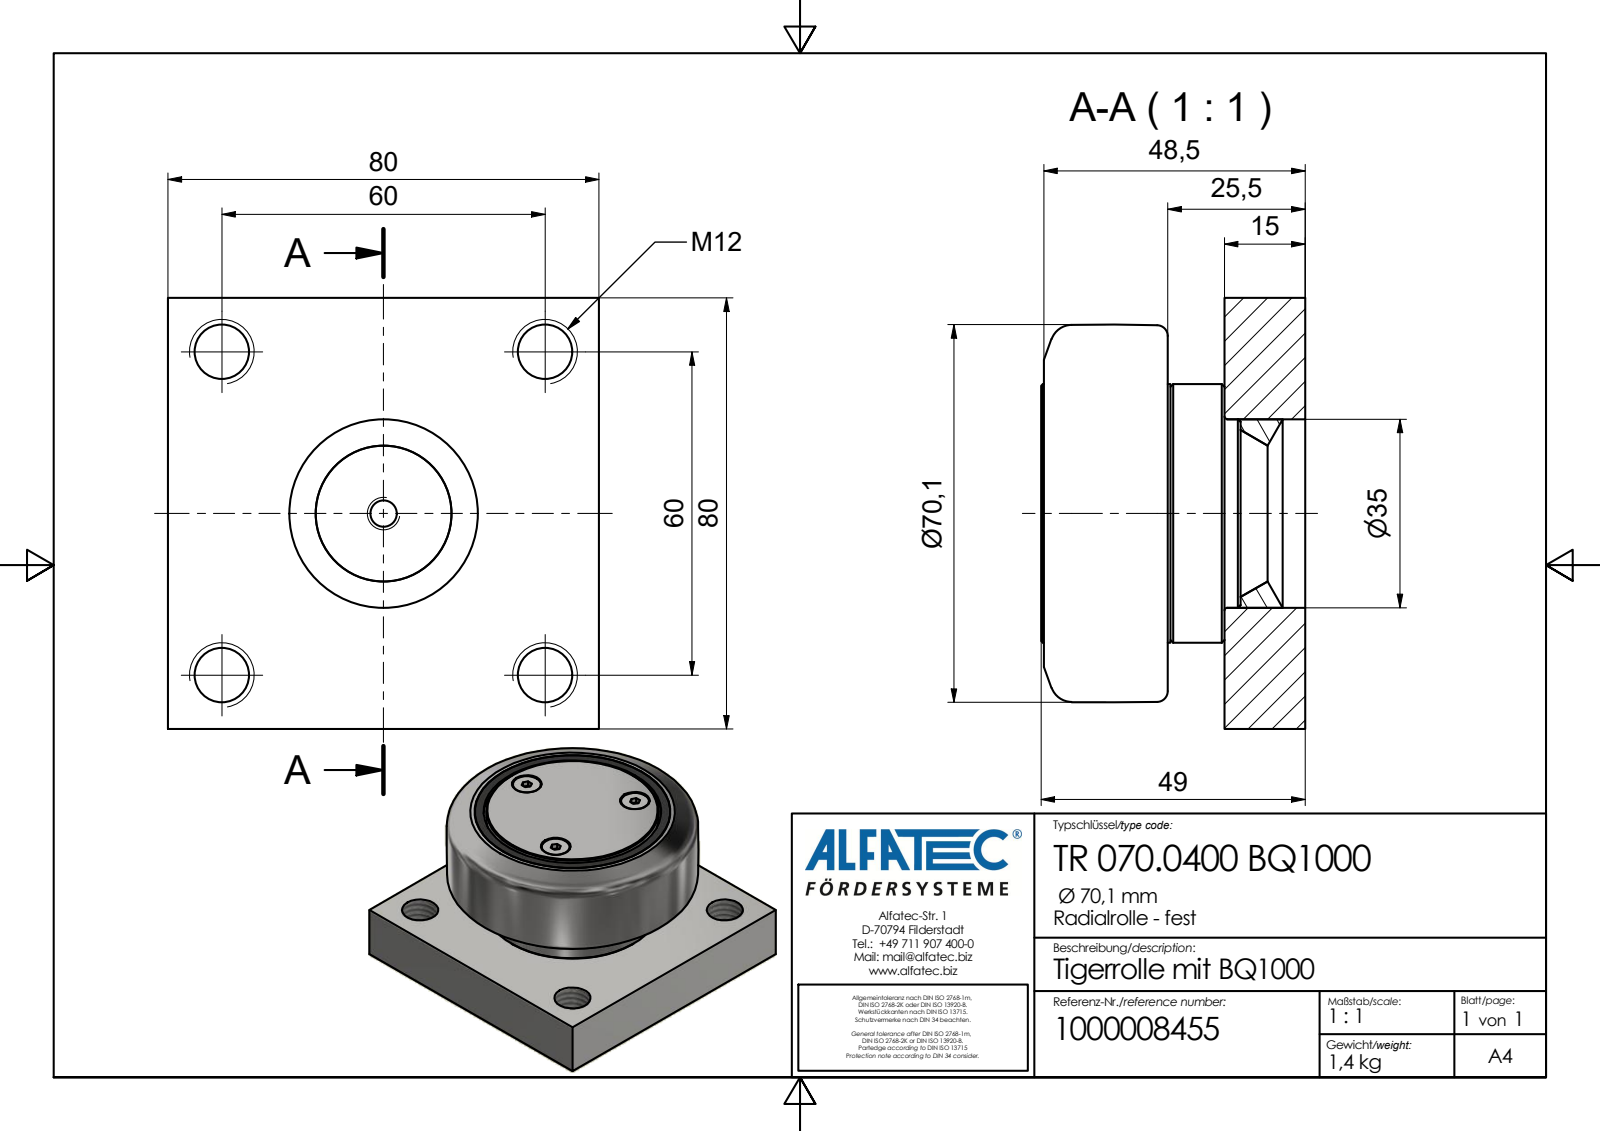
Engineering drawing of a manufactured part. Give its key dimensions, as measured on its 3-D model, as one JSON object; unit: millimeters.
{"part_name": "XTR 070.0400 BQ1000_Kontur", "step_written_by": "Autodesk Inventor 2020 (AP242_MANAGED_MODEL_BASED_3D_ENGINEERING_MIM_LF)", "units": "millimeters", "bodies": {"solids": 1, "faces": 62, "planar": 39, "cylindrical": 15, "other": 8}, "overall_size": [80, 80, 49], "volume_mm3": 199584, "surface_area_mm2": 30864, "round_holes": [[10.11, 4], [8.3, 3], [4.92, 1], [35, 1]], "round_bosses_or_shafts": [[7.8, 3], [48, 1]], "face_to_face_distances": [15, 80, 25.5, 10.5, 23.5, 49, 34, 0.5, 48.5, 33.5], "hole_center_spacings": [60, 42.43, 18, 31.18, 25.47, 32.31, 41.58, 50.19]}
